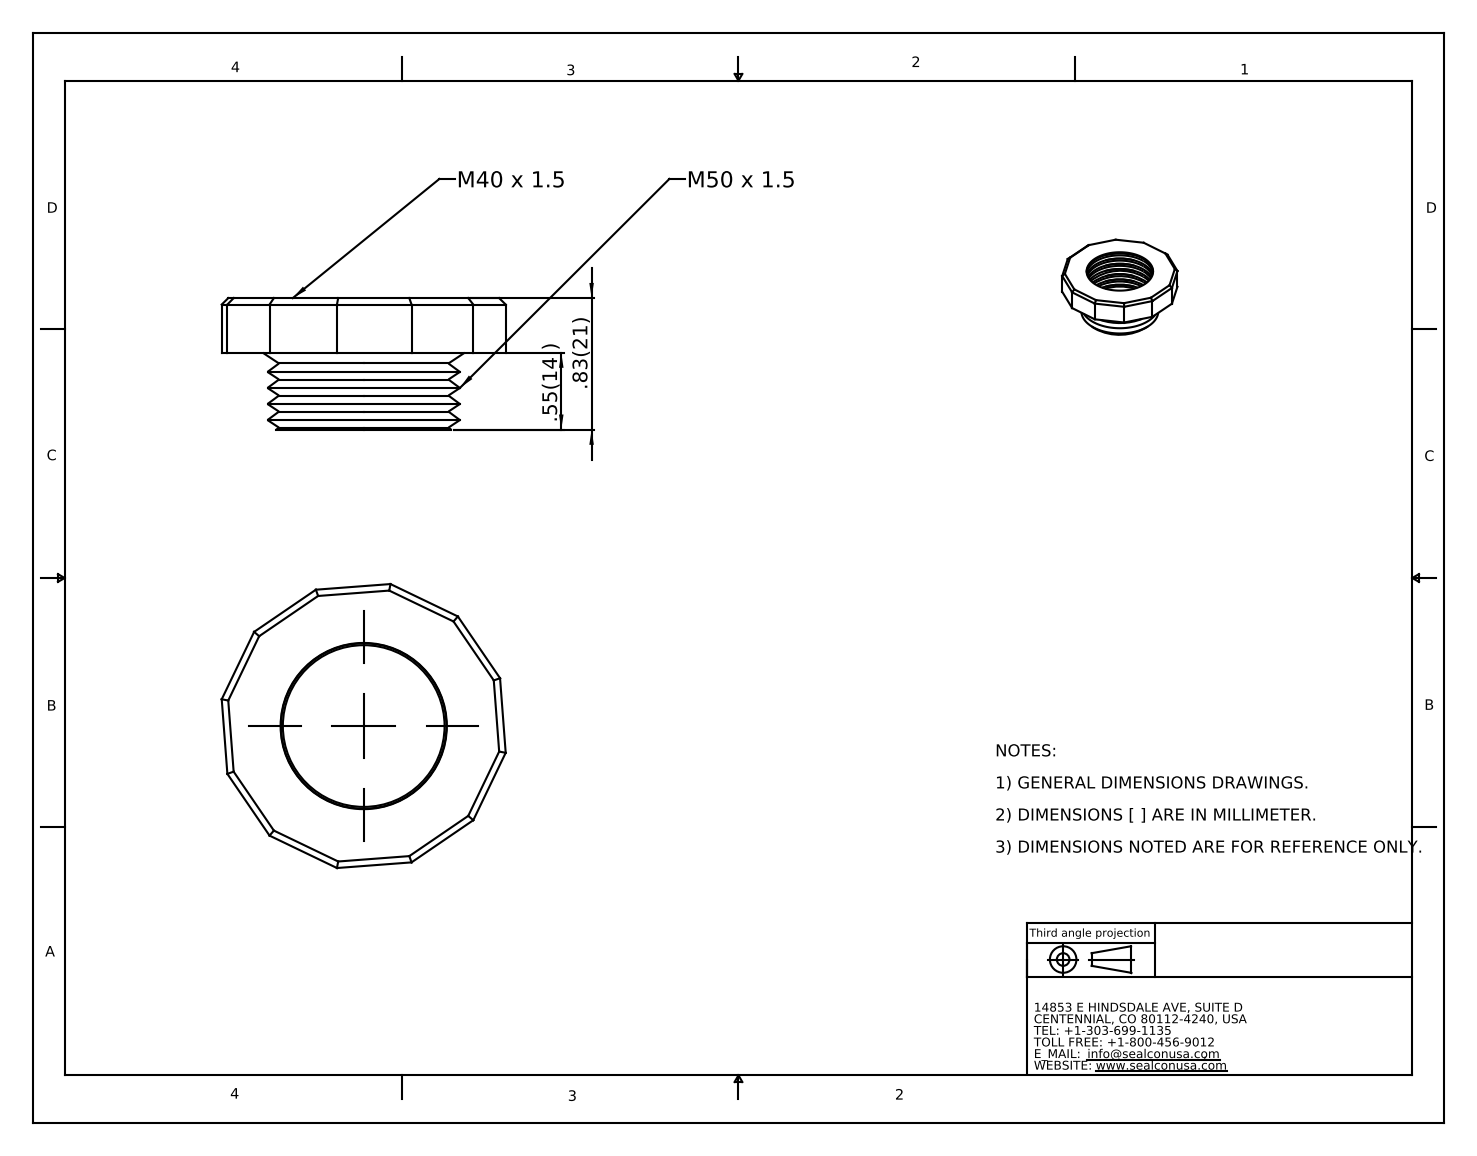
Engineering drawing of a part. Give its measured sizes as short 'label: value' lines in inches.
name: RR-5040-GY
written by: SolidWorks 2008 (CONFIG_CONTROL_DESIGN)
unit: in
bodies: 1 solid, 93 faces (27 planar, 16 cylindrical, 50 other)
size: 0.885 × 0.885 × 0.41
volume: 0.077 in³; area: 2.673 in²
holes: 1× ⌀0.504, 1× ⌀0.518
face distances: 0.17, 0.869, 0.87, 0.24, 0.41
